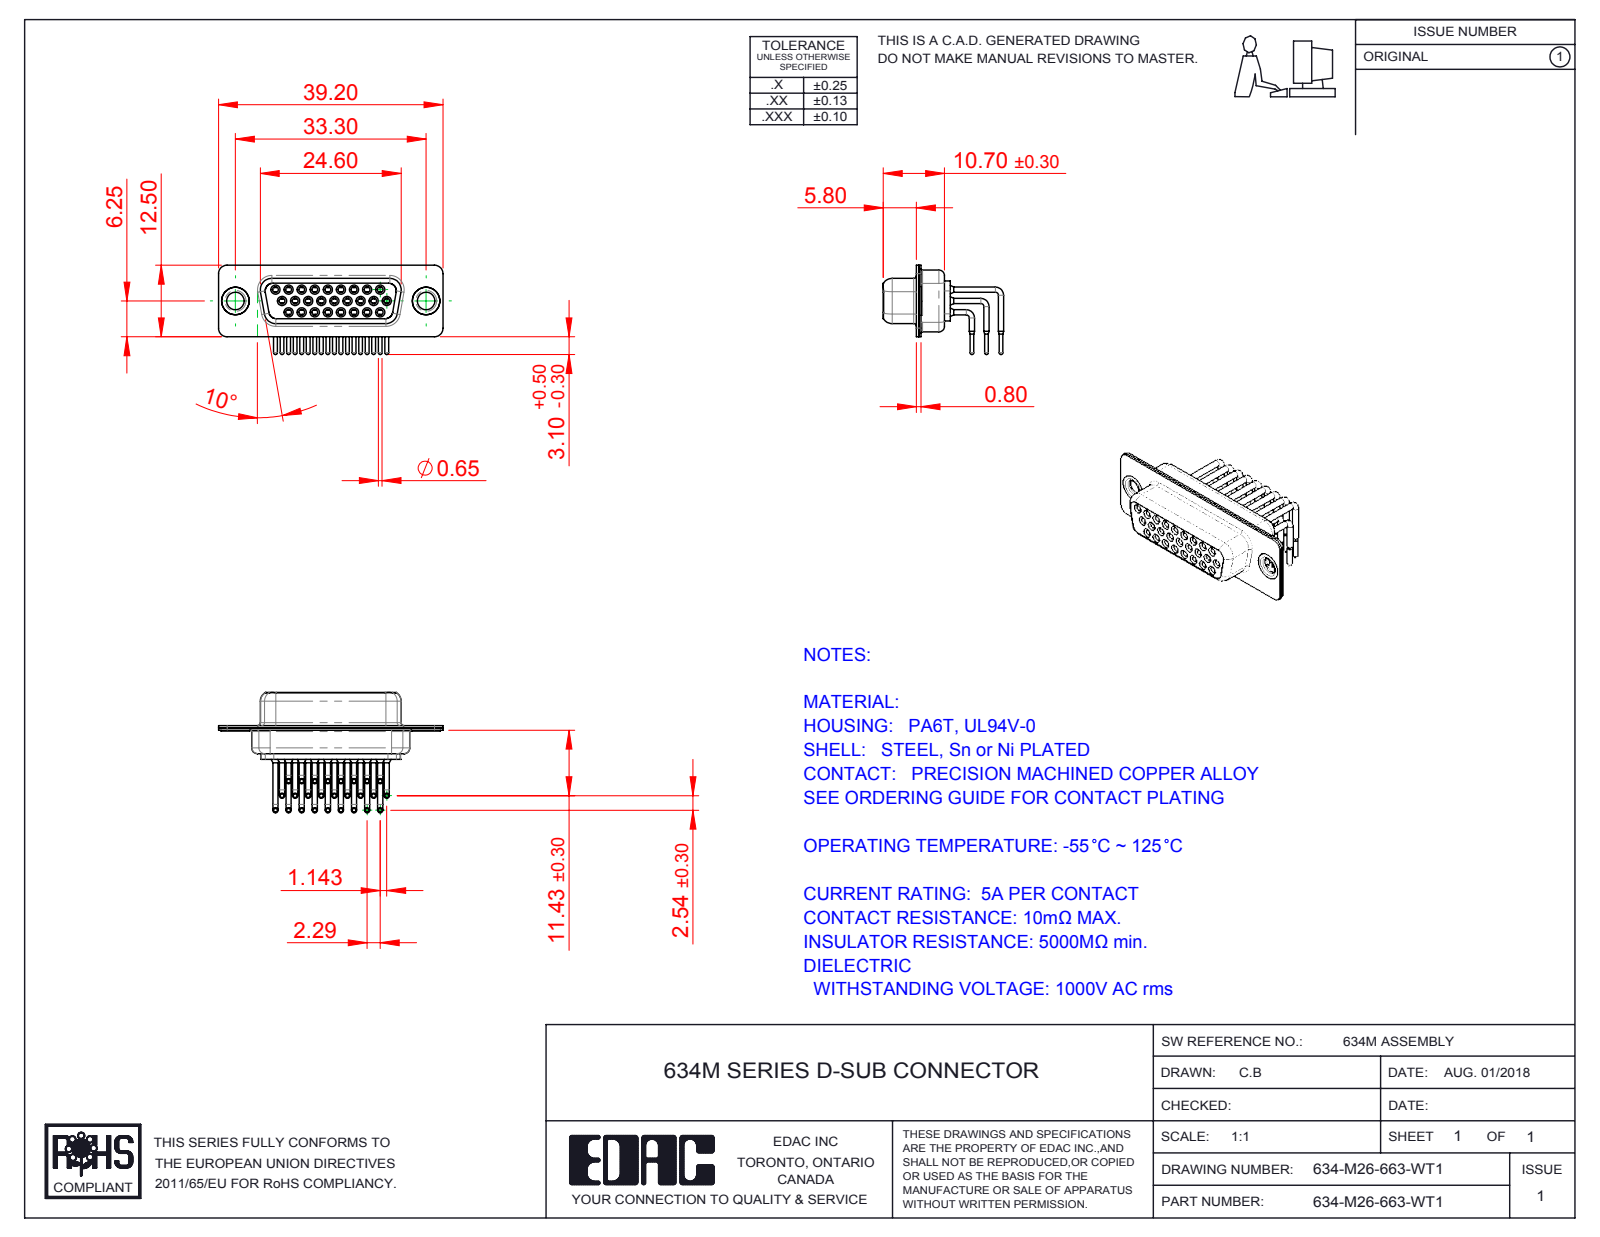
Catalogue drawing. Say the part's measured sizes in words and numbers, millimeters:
The part is named "634M Housing_26 Contacts; 634M Thru Hole Rivet; 634M Contact Row 2; 634M Shell Rear_26 Contacts (+4 more)". Its 3-D file was written by "SolidWorks 2016 (CONFIG_CONTROL_DESIGN)". It is 31 solids with 1631 faces: 457 planar, 719 cylindrical and 455 other. Overall it measures 39.2 by 21.02 by 15.6 millimeters. Its volume is 2 454 cubic millimeters and its surface area 8 321 square millimeters. Round holes: 26 of diameter 1, 26 of diameter 1.1, 26 of diameter 1.7, 26 of diameter 1.8, 26 of diameter 2, 2 of diameter 3.05, 2 of diameter 4, 2 of diameter 4.8. Round bosses or shafts: 52 of diameter 0.9, 26 of diameter 1.6, 26 of diameter 1.5, 26 of diameter 0.65, 2 of diameter 5, 2 of diameter 4.9, 2 of diameter 3.55, 1 of diameter 2. Partial cylindrical surfaces (rounded edges, fillets, slot ends): 16 of radius 1.5, 12 of radius 2, 8 of radius 1.35, 8 of radius 1.6, 4 of radius 0.25, 4 of radius 0.5, 4 of radius 0.6, 4 of radius 0.65. The main face-to-face distances are 0.4, 1.45, 8.95, 8.5, 1.9, 2.3, 0.8, 6.2, 0.45, 7.05. The hole center spacings are 3.96, 2.28, 4.57, 6.05, 2.29, 8.24, 6.86, 6.04.
